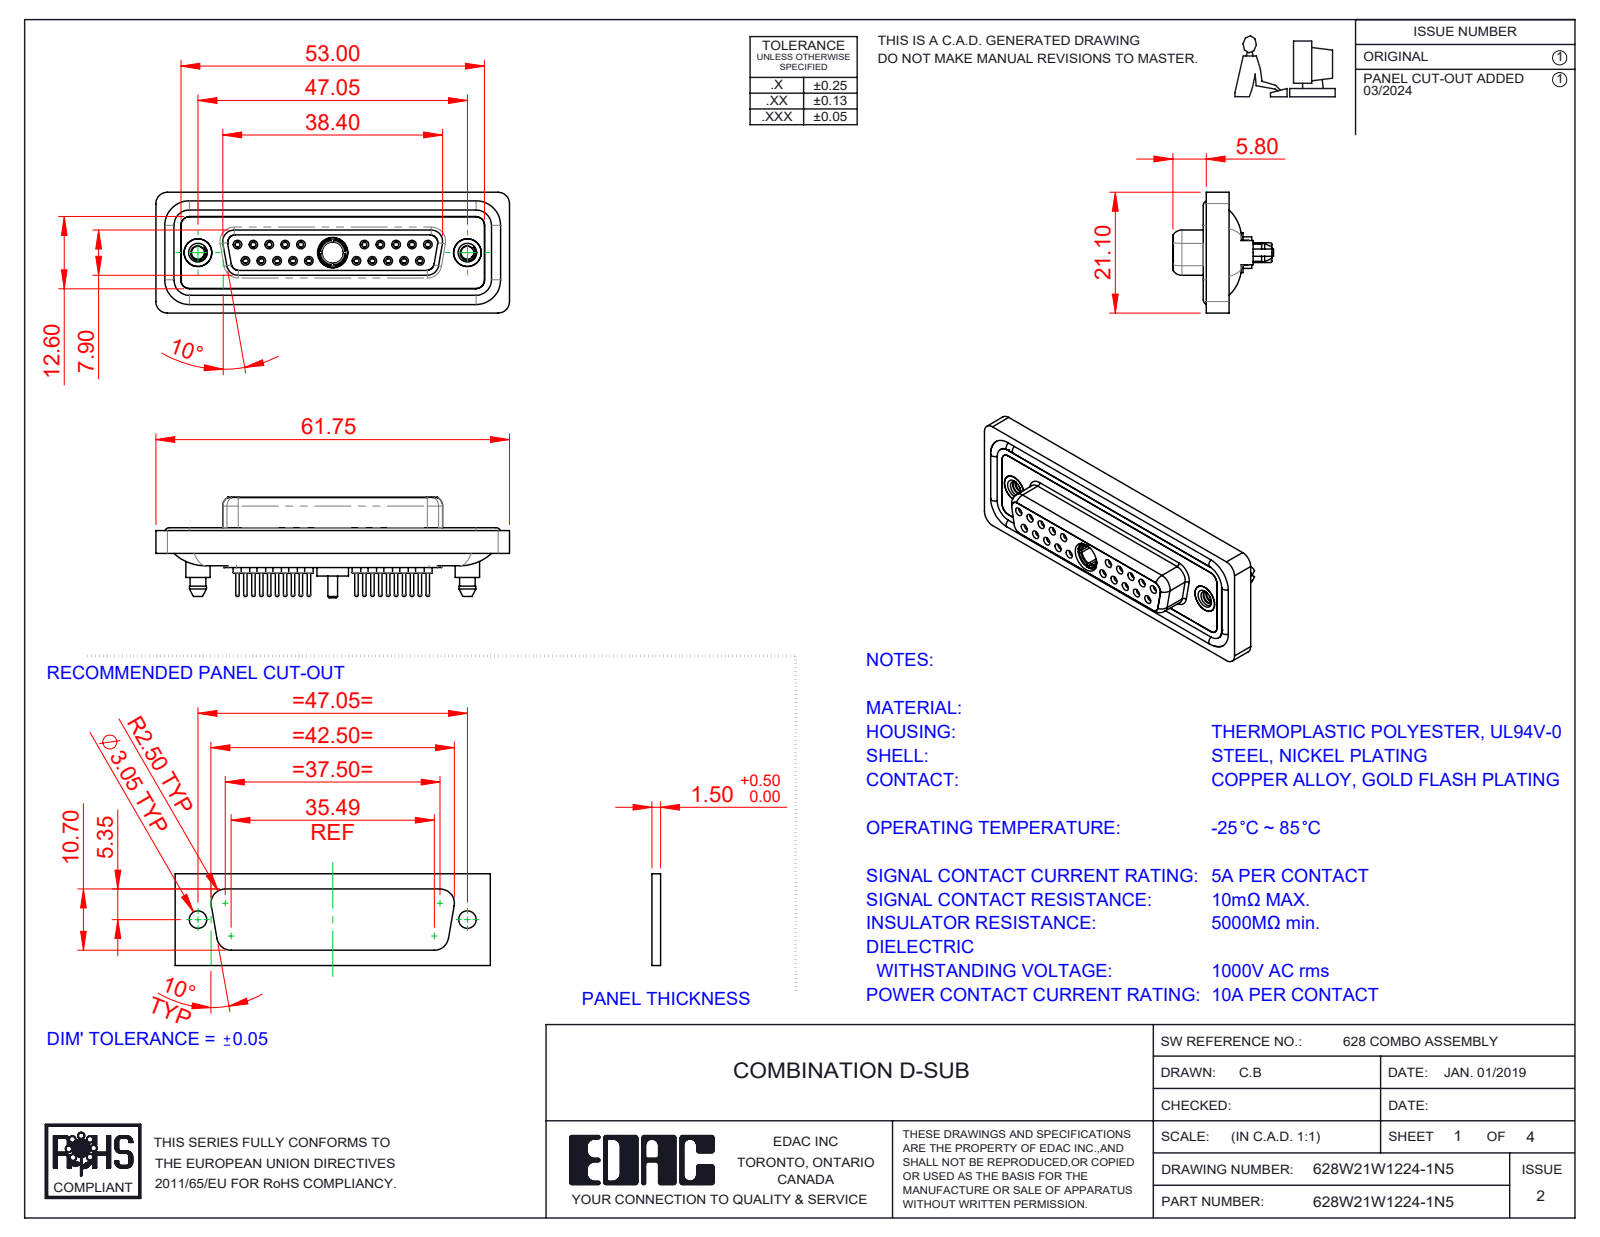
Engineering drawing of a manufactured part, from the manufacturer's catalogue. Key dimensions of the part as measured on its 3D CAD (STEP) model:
Part name (STEP PRODUCT): 628Combo Shell Rear_25 Contacts; 628Combo Shell Front_25 Contacts; 628Combo Waterproof Housing_25 Contacts; Power Socket_10A S (+5 more)
STEP written by: SolidWorks 2023 (CONFIG_CONTROL_DESIGN)
Units: millimetres
Bodies: 29 solids, 1610 faces (450 planar, 623 cylindrical, 537 other)
Overall size (bounding box): 61.75 × 21.1 × 17.55
Volume: 8 493 mm³ · Surface area: 14 322 mm²
Round holes (diameter × count): ⌀0.9 ×20, ⌀1.1 ×20, ⌀1.5 ×20, ⌀2 ×20, ⌀1.6 ×10, ⌀1.7 ×10, ⌀4.85 ×3, ⌀2.26 ×2, ⌀4 ×2, ⌀4.05 ×2, ⌀5 ×2, ⌀3.7 ×1
Round bosses / shafts (diameter × count): ⌀2.2 ×20, ⌀0.6 ×20, ⌀1.6 ×14, ⌀5.4 ×2, ⌀4.95 ×2, ⌀4.8 ×2, ⌀4.25 ×2, ⌀5.5 ×1
Partial cylindrical surfaces — rounded edges, fillets, slot ends (radius × count): R1.5 ×24, R2 ×18, R1.6 ×10, R1.35 ×8, R0.25 ×4, R0.5 ×4, R0.6 ×4, R0.65 ×4
Main face-to-face distances: 0.4, 1.8, 7.45, 6.6, 5.65, 1.6, 0.5, 7.05, 2.9, 1.1
Hole centre spacings: 3.16, 2.77, 5.54, 5.03, 8.31, 7.48, 16.62, 19.39
